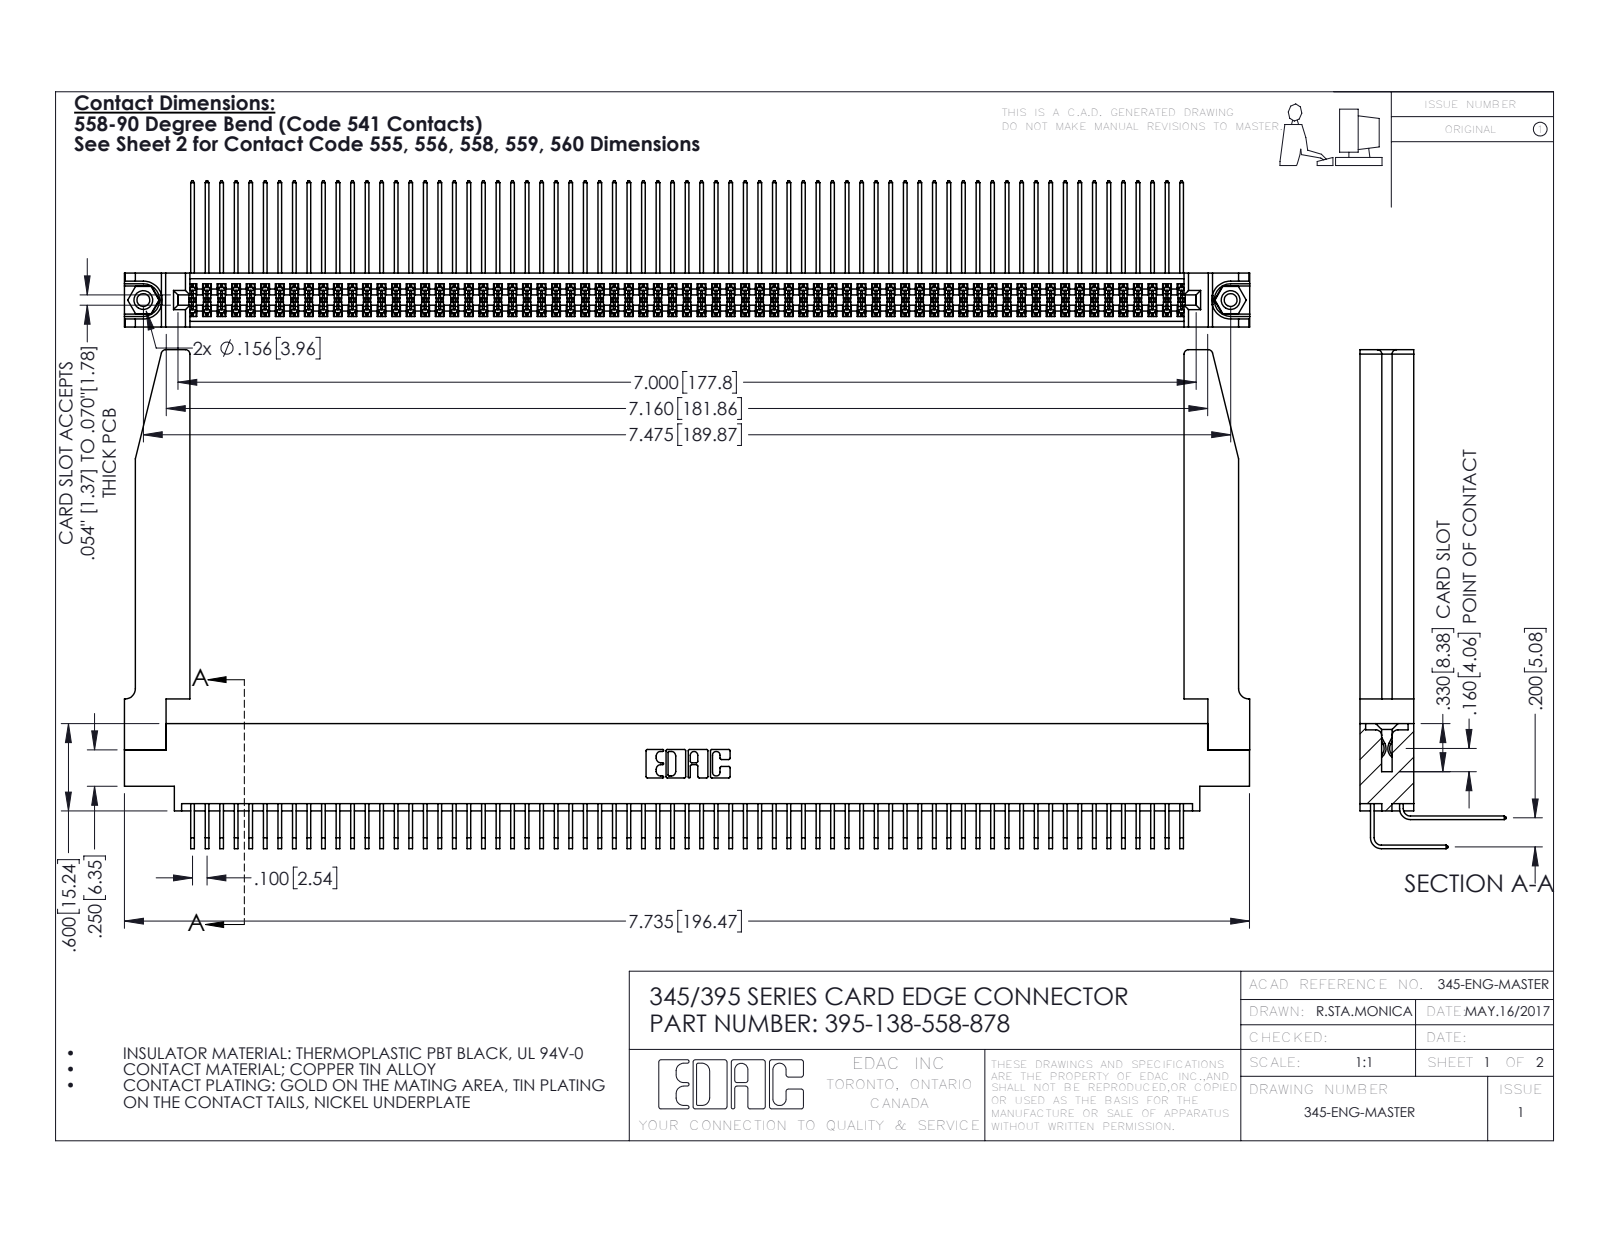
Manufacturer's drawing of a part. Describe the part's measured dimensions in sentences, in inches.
The part is named "395-138-558-878; 345-292-001_558 559 Tail - 1; 345-220-078_345-220-078; 345-250-001_345-250-001-102 (+2 more)". Its 3-D file was written by "SolidWorks 2016 (CONFIG_CONTROL_DESIGN)". It is 143 solids with 7540 faces: 5056 planar, 2432 cylindrical and 52 other. Overall it measures 7.736 by 3.429 by 1.005 inches. Its volume is 1.696 cubic inches and its surface area 63.31 square inches. Round holes: 2 of diameter 0.089, 2 of diameter 0.125, 2 of diameter 0.156, 1 of diameter 0.064. Round bosses or shafts: 2 of diameter 0.155. Partial cylindrical surfaces (rounded edges, fillets, slot ends): 275 of radius 0.006, 22 of radius 0.01, 8 of radius 0.03, 6 of radius 0.007, 6 of radius 0.031, 3 of radius 0.026, 2 of radius 0.014, 2 of radius 0.019. The main face-to-face distances are 0.072, 0.298, 0.37, 0.2, 0.098, 0.272, 0.025, 0.225, 0.175, 0.025. The hole center spacings are 0.27, 7.239, 7.475.
